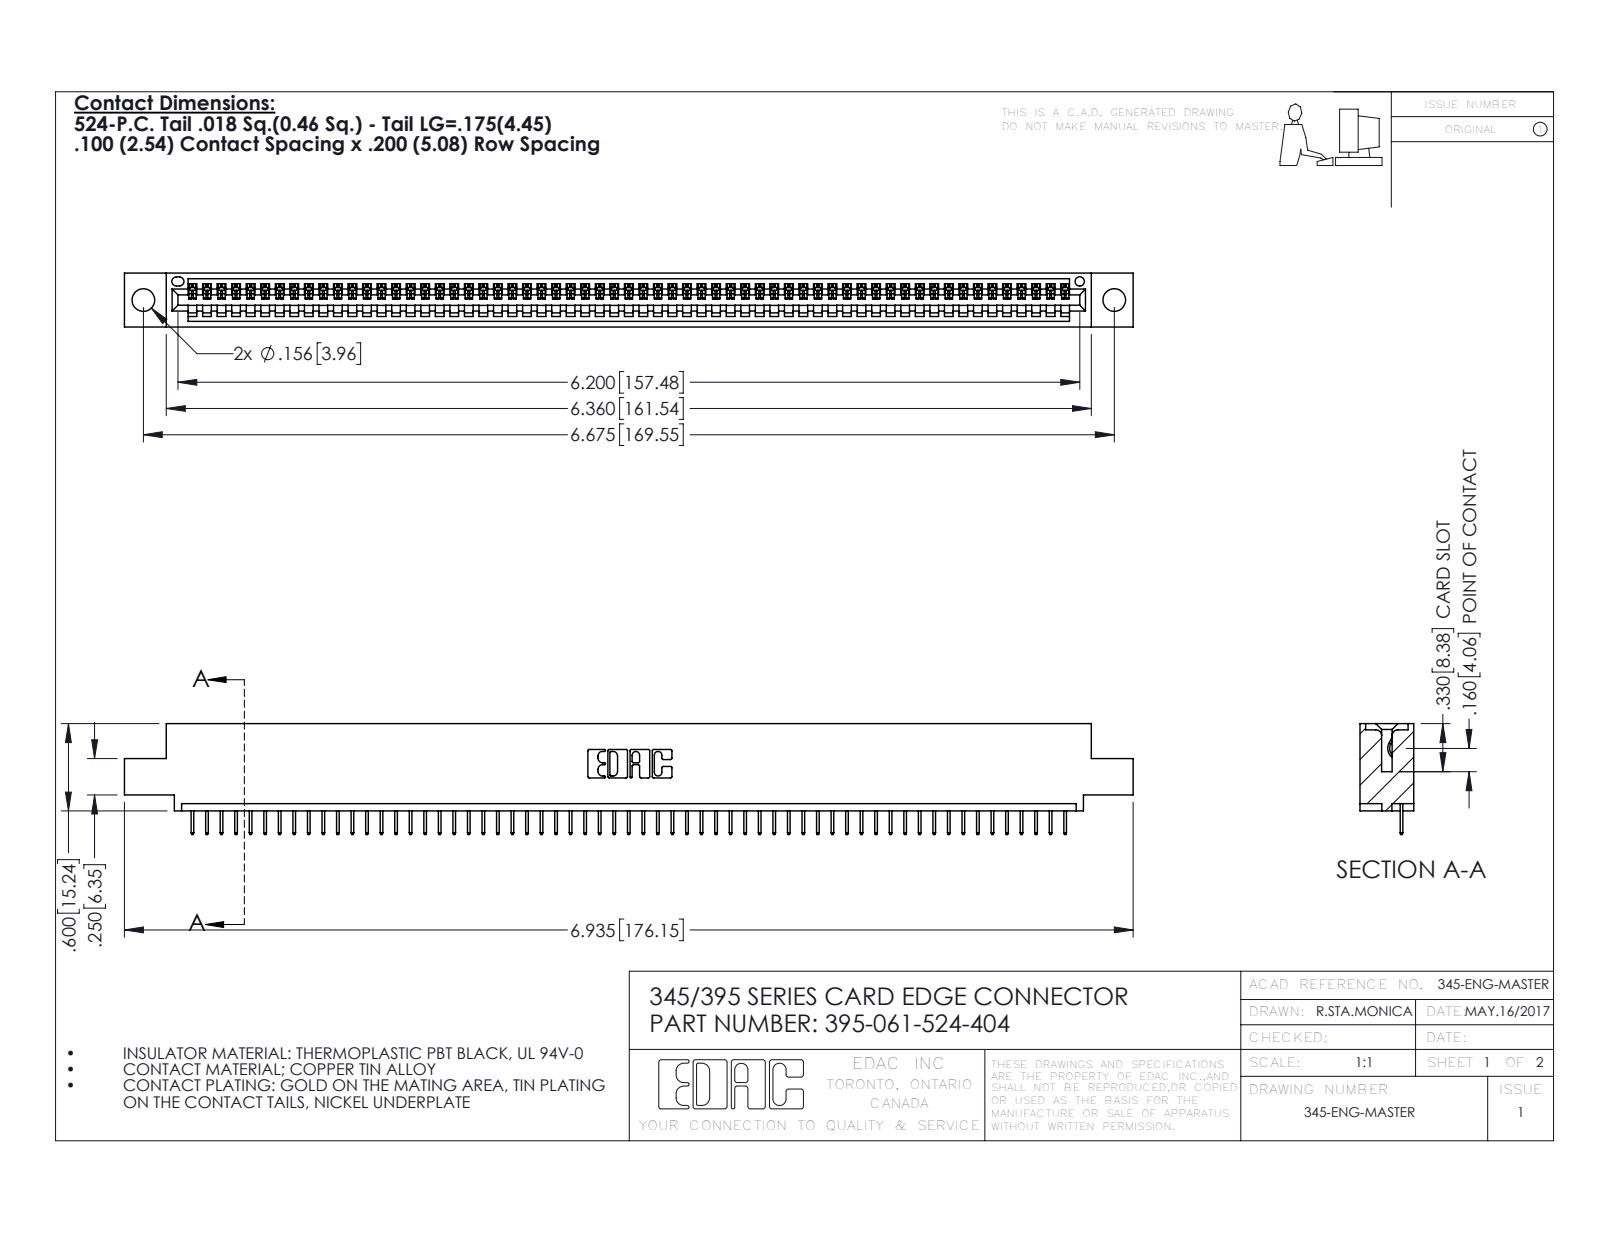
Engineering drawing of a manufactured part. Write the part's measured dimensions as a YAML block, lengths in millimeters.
part_name: "345-292-001_345-293-124; 345 Part_0.110 Offset - 0.156 Dia-TH; 395-061-524-404"
step_written_by: "SolidWorks 2016 (CONFIG_CONTROL_DESIGN)"
units: millimeters
bodies: {solids: 62, faces: 3912, planar: 2890, cylindrical: 1022, other: 0}
overall_size: [176.1, 19.4, 9.4]
volume: 16490
surface_area: 21280
round_holes:
  - {diameter: 4, count: 2}
  - {diameter: 1.6, count: 1}
partial_cylinders:
  - {radius: 0.2, count: 122}
  - {radius: 0.3, count: 22}
  - {radius: 0.2, count: 6}
  - {radius: 0.8, count: 6}
  - {radius: 0.7, count: 3}
  - {radius: 0.8, count: 2}
  - {radius: 1, count: 2}
  - {radius: 0.4, count: 1}
face_to_face_distances: [1.8, 7.6, 9.4, 5.1, 2.5, 6.9, 0.6, 5.7, 1.8, 3.8]
hole_center_spacings: [6.9, 163.6, 169.5]
